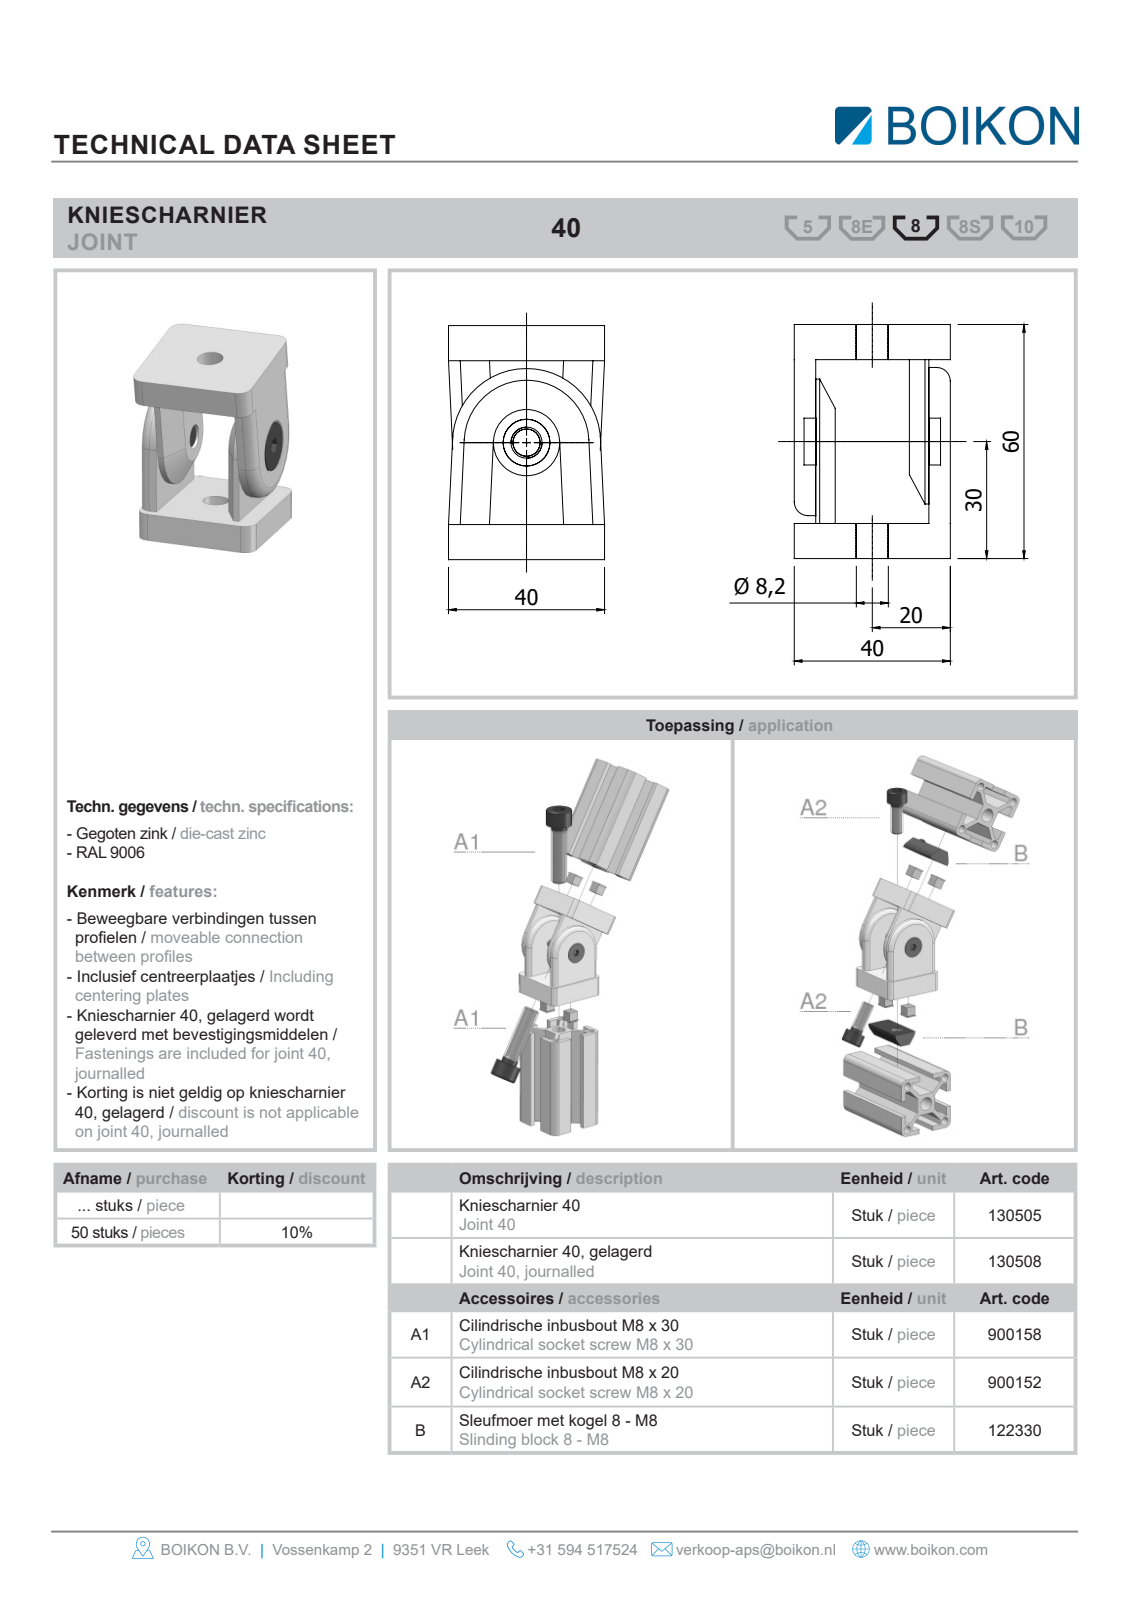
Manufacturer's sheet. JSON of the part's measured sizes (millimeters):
{"part_name": "Root; 130505Scharnier 40BOIKON; 900612Verz. inbusbout DIN 7991 EV M8 x 12Countersunk head bolts0", "step_written_by": "HiCAD 2013 1802.4 Build 509 (AUTOMOTIVE_DESIGN)", "units": "millimeters", "bodies": {"solids": 4, "faces": 94, "planar": 52, "cylindrical": 32, "other": 10}, "overall_size": [60, 40, 40], "volume_mm3": 51382, "surface_area_mm2": 20726, "round_holes": [[8, 1], [8.5, 1], [9, 1], [26, 1]], "round_bosses_or_shafts": [[34, 1], [32, 1], [16, 1], [6.47, 1]], "partial_cylinders_radius": [[3.5, 4], [4, 4]], "face_to_face_distances": [34, 6, 9, 51, 40, 28, 60, 42, 12.6, 27.4]}
